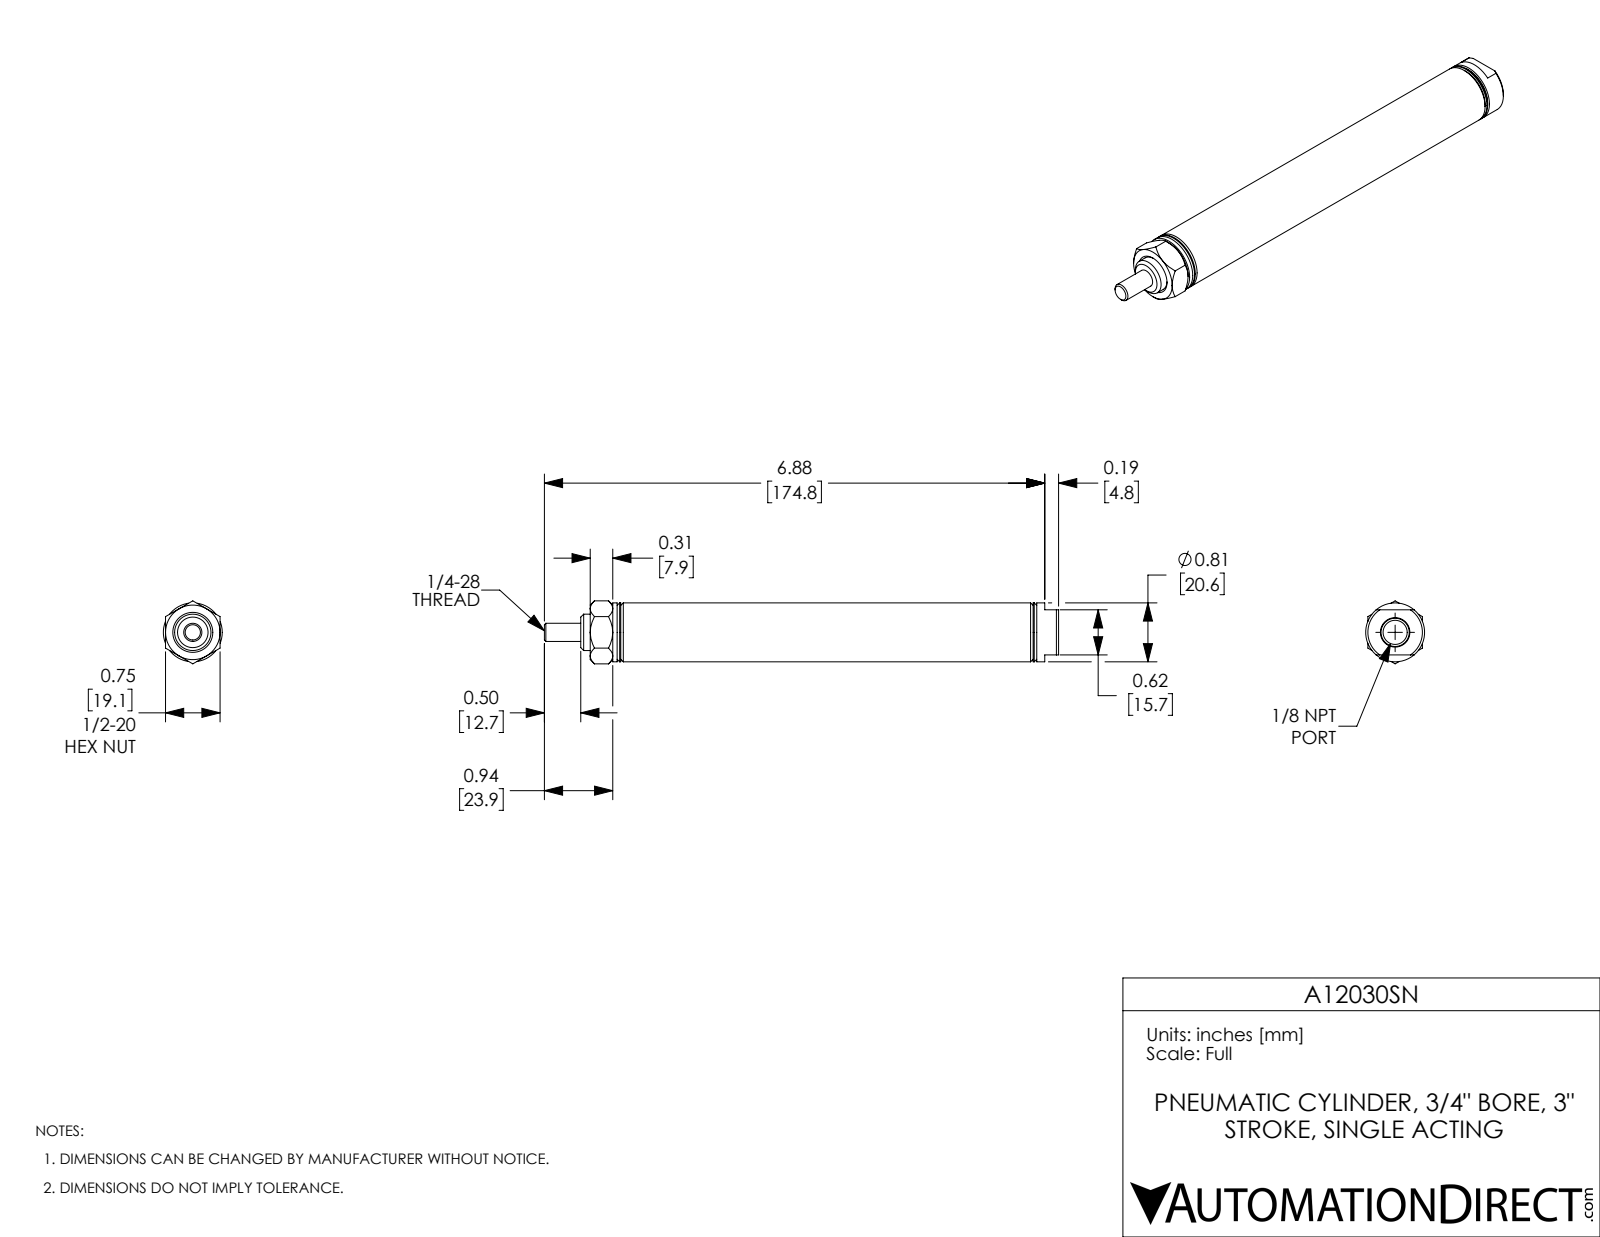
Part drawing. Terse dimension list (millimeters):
name: A12030SN_Mounting Nut_D-98; A12030SN-Rod; A12030SN-MainBody; A12030SN
written by: SolidWorks 2017 (AUTOMOTIVE_DESIGN)
unit: mm
bodies: 3 solids, 82 faces (25 planar, 24 cylindrical, 33 other)
size: 179.6 × 22 × 20.6
volume: 33 330 mm³; area: 24 060 mm²
holes: 1× ⌀6.4, 1× ⌀8.4, 1× ⌀12.7, 1× ⌀19.1
bosses: 1× ⌀20.6
face distances: 122.3, 33.4, 12.7, 109.6, 88.9, 76.2, 46.1, 155.7, 19.1, 163.6
